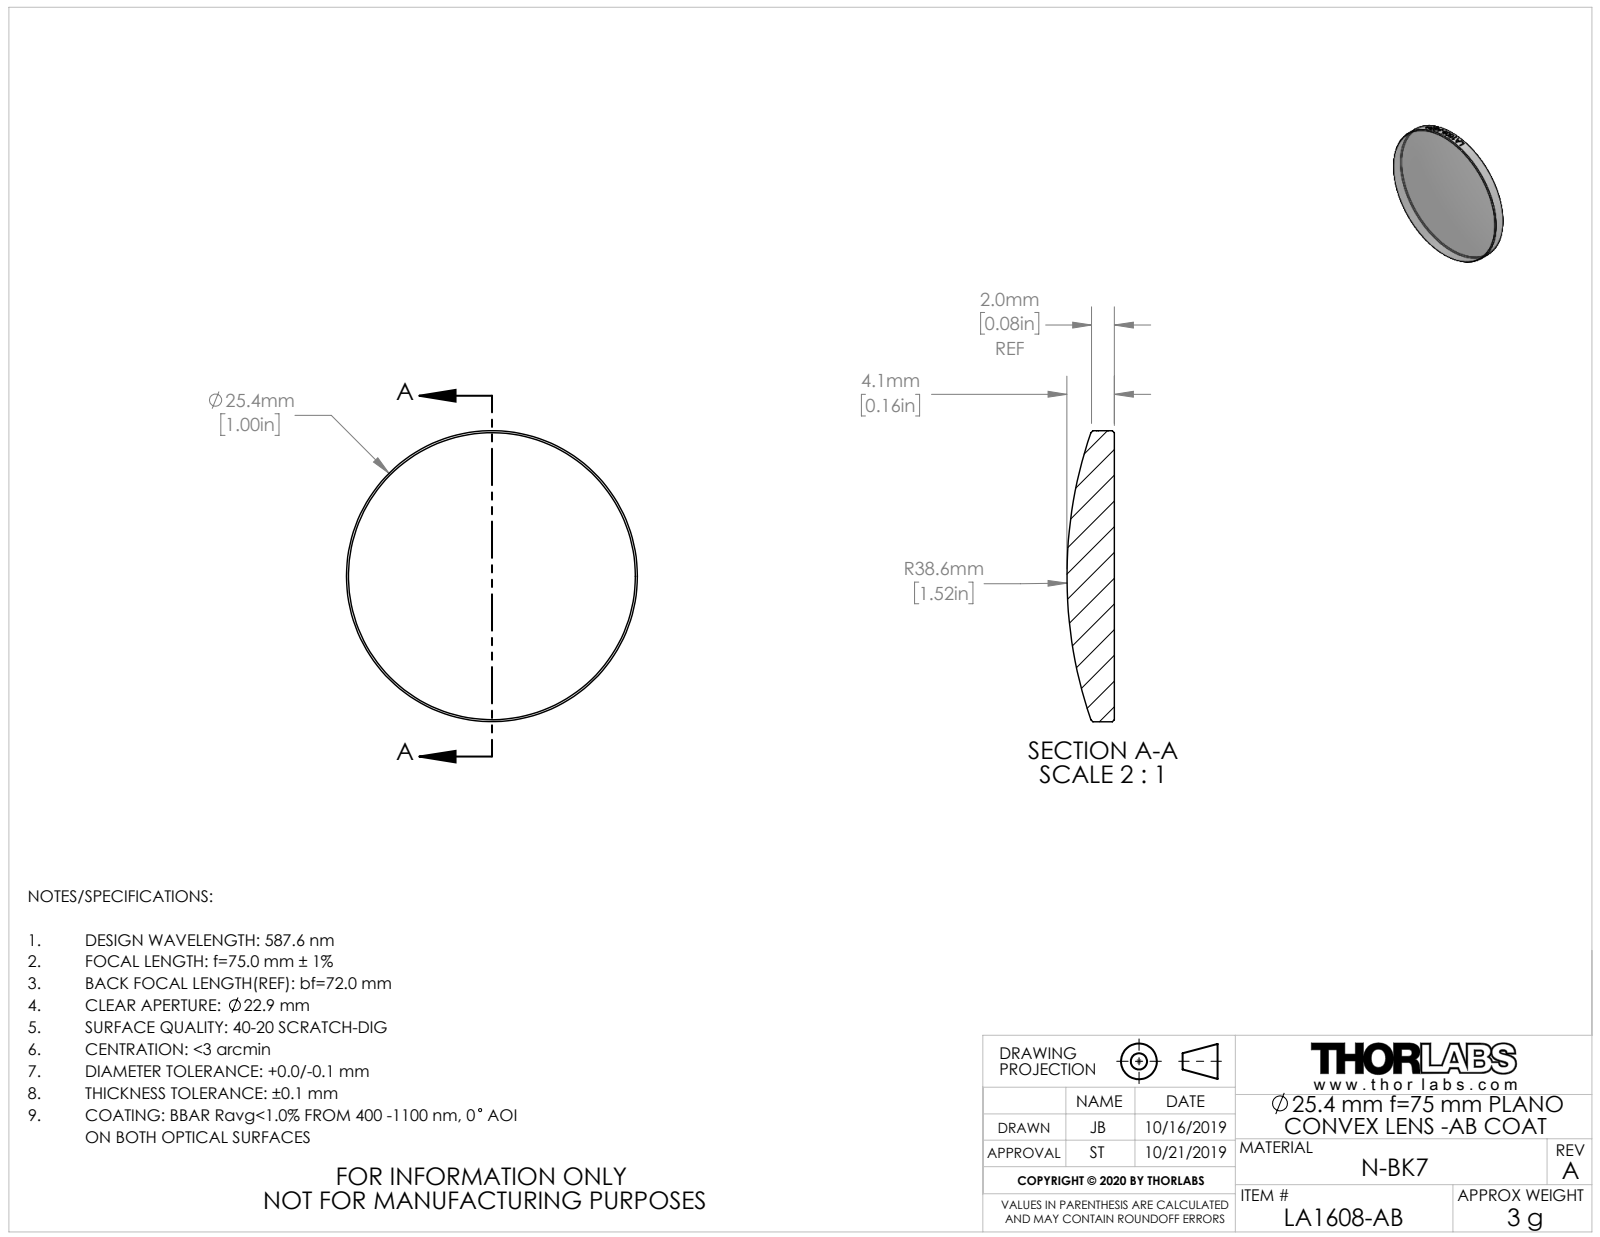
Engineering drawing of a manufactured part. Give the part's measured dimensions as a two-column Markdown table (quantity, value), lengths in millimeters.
| quantity | value |
| --- | --- |
| part name | TTN195788-E0W |
| STEP written by | SolidWorks 2018 (CONFIG_CONTROL_DESIGN) |
| units | millimeters |
| bodies | 1 solid, 30 faces (1 planar, 23 cylindrical, 6 other) |
| overall size | 25.4 × 25.4 × 4.1 |
| volume | 1 600 mm³ |
| surface area | 1 174 mm² |
| round bosses / shafts (diameter × count) | 25.4 × 1 |
